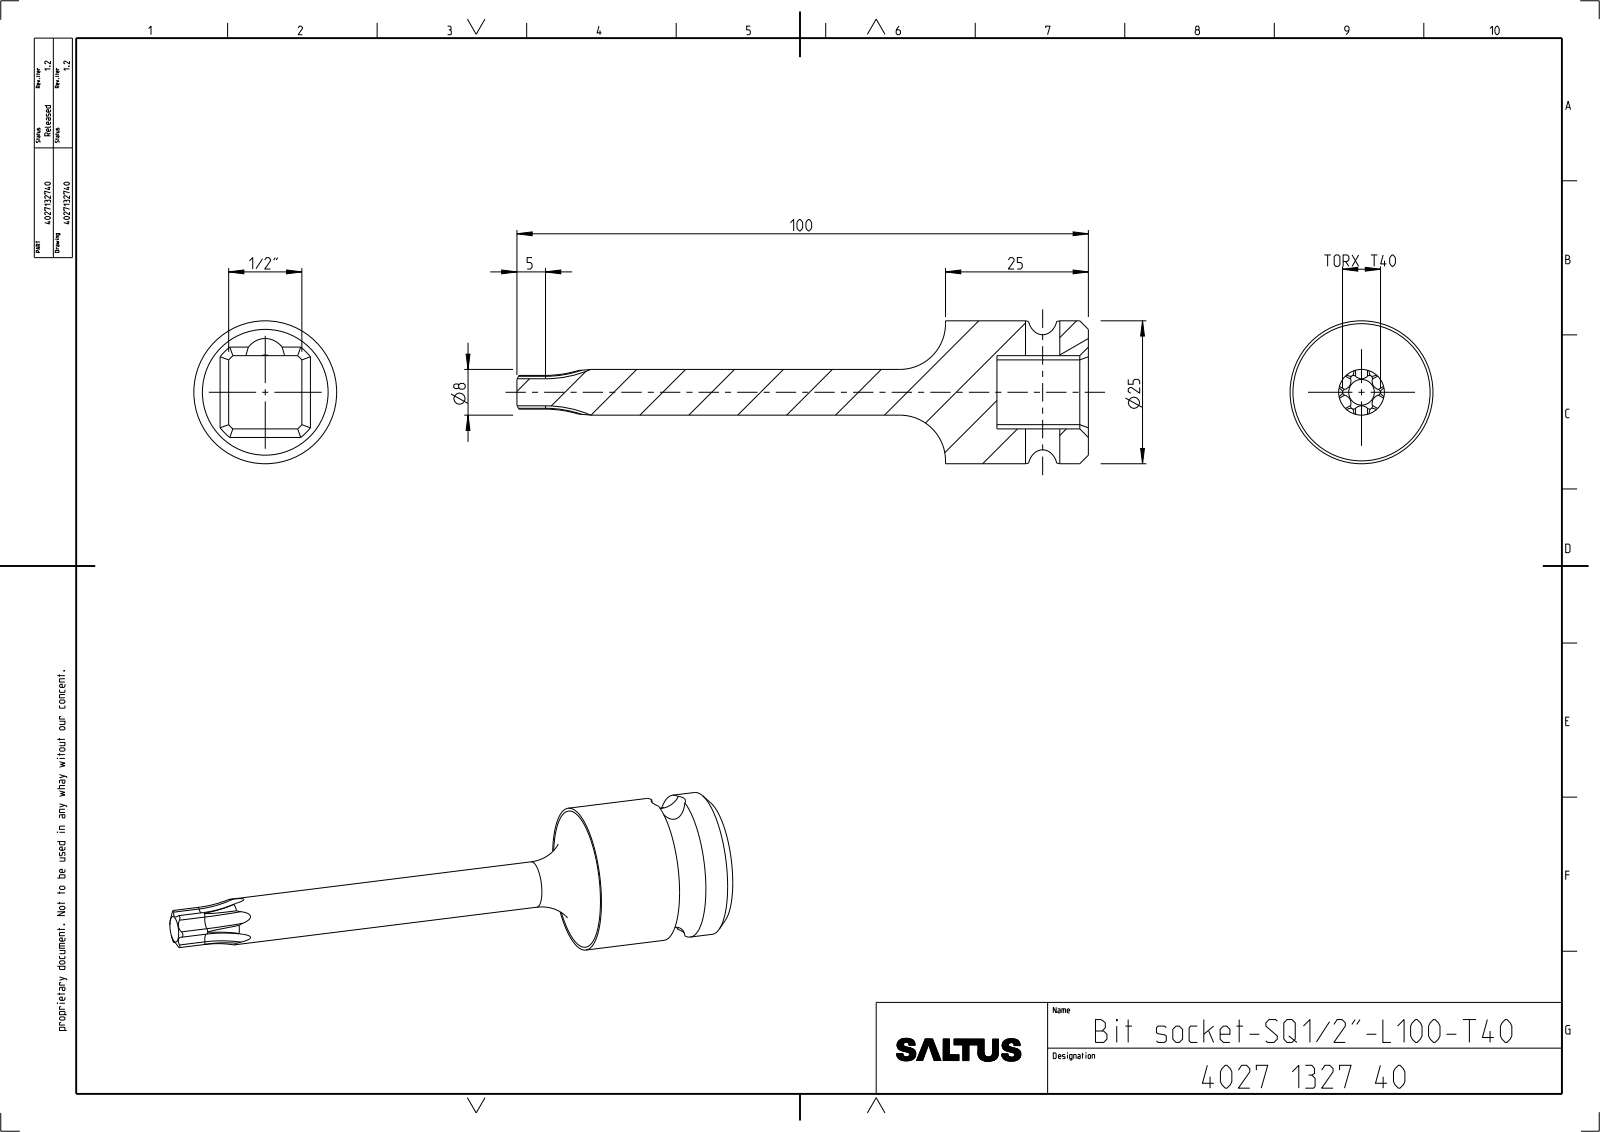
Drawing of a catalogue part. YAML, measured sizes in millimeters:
part_name: "4027132740"
step_written_by: "CREO PARAMETRIC BY PTC INC, 2022414 (CONFIG_CONTROL_DESIGN)"
units: millimeters
bodies: {solids: 1, faces: 82, planar: 13, cylindrical: 33, other: 36}
overall_size: [100, 25, 25]
volume: 12710
surface_area: 5557
round_holes:
  - {diameter: 6, count: 1}
round_bosses_or_shafts:
  - {diameter: 25, count: 1}
  - {diameter: 8, count: 1}
partial_cylinders:
  - {radius: 0.51, count: 6}
  - {radius: 1.47, count: 6}
  - {radius: 3.33, count: 1}
  - {radius: 4, count: 1}
  - {radius: 8.55, count: 1}
face_to_face_distances: [12.82, 16, 25, 9, 100, 84, 75]
